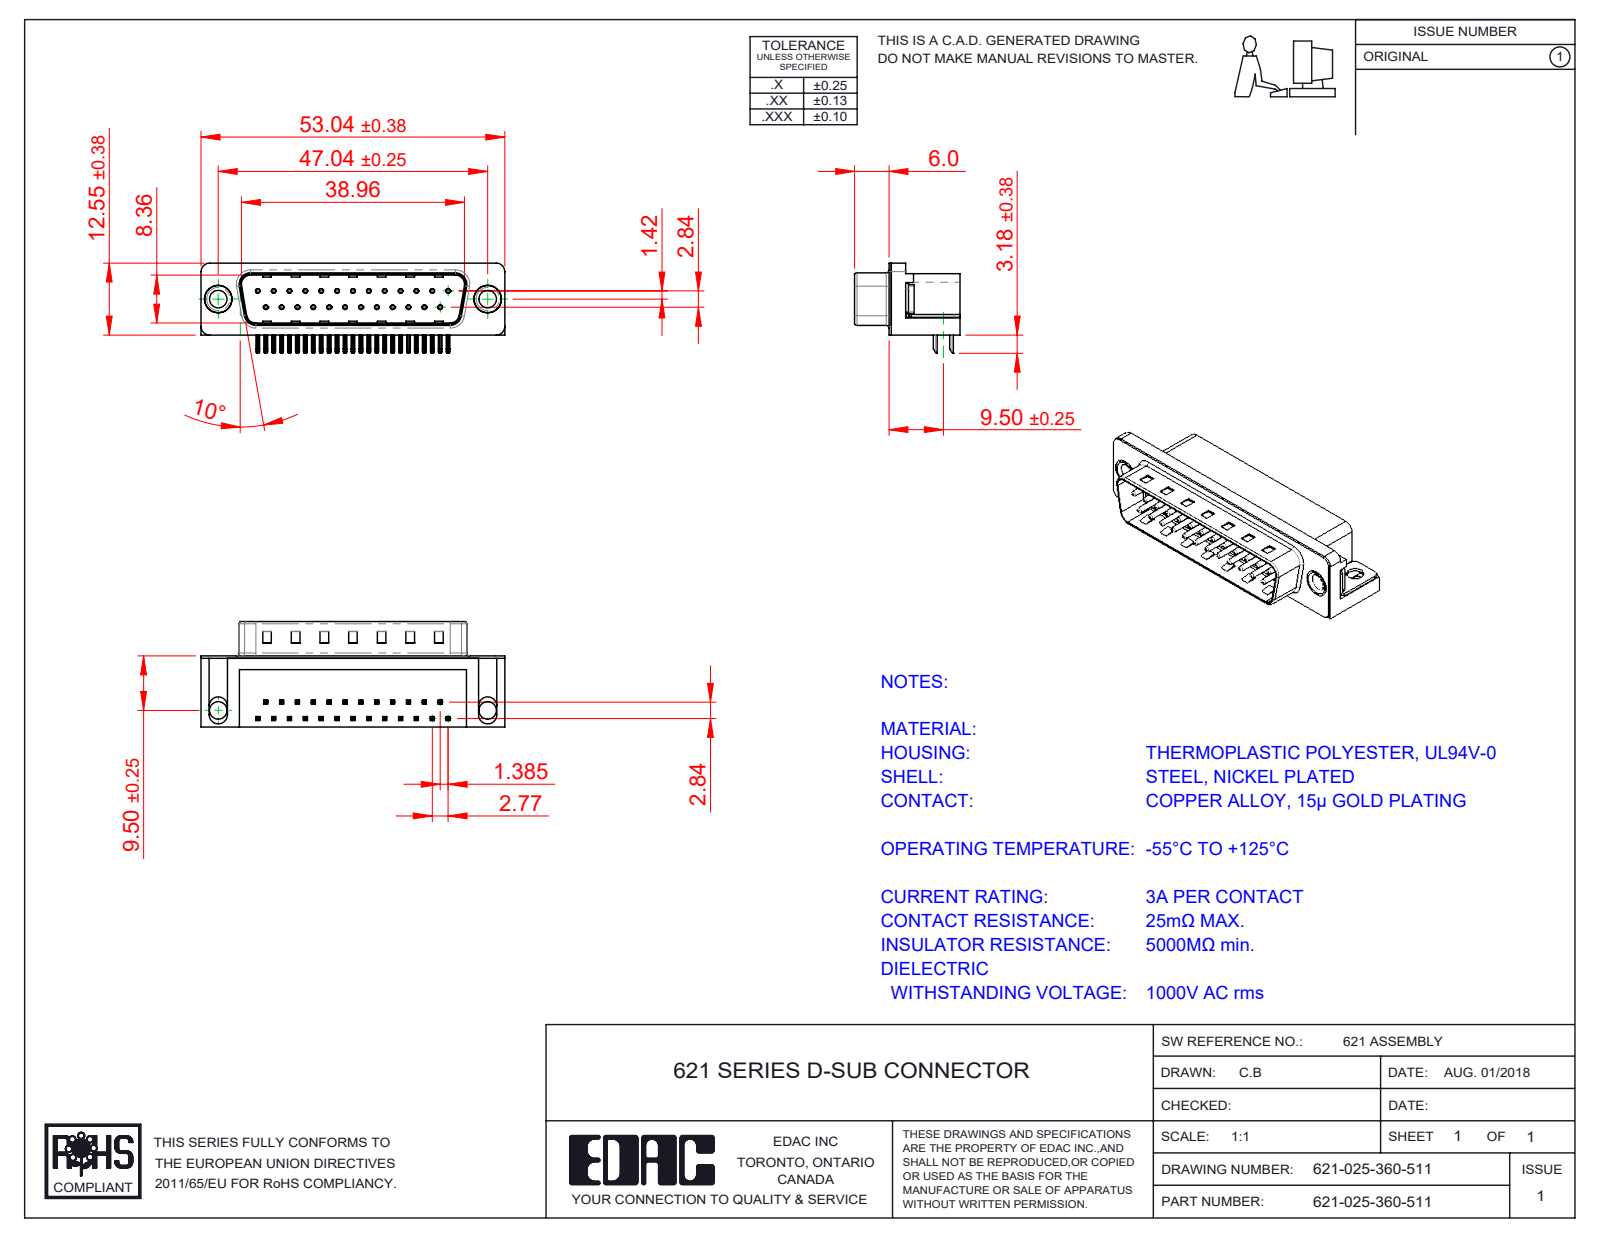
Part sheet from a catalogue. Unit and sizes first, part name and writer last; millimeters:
Units: millimetres
Overall size (bounding box): 53.04 × 18.4 × 15.73
Round holes (diameter × count): ⌀0.35 ×25, ⌀0.8 ×25, ⌀3.05 ×4, ⌀4 ×2, ⌀4.8 ×2, ⌀5 ×2
Round bosses / shafts (diameter × count): ⌀0.75 ×25, ⌀4.9 ×2, ⌀4.75 ×2, ⌀3.85 ×2
Partial cylindrical surfaces — rounded edges, fillets, slot ends (radius × count): R0.25 ×108, R0.12 ×50, R1 ×16, R0.5 ×9, R1.6 ×8, R1.5 ×7, R0.9 ×4, R2 ×4
Main face-to-face distances: 0.4, 12, 10.35, 2.1, 8.76, 10.46, 1.7, 10.86, 12.4, 9
Hole centre spacings: 3.16, 2.77, 5.54, 8.31, 11.08, 13.85, 16.62, 5.03
Volume: 6 333 mm³ · Surface area: 7 646 mm²
Bodies: 31 solids, 2221 faces (1403 planar, 641 cylindrical, 177 other)
Part name (STEP PRODUCT): 621 Contact Top; 621 Thru Hole Rivet; 621-025-360-511; 621 Shell_25 Socket (+3 more)
STEP written by: SolidWorks 2016 (CONFIG_CONTROL_DESIGN)
